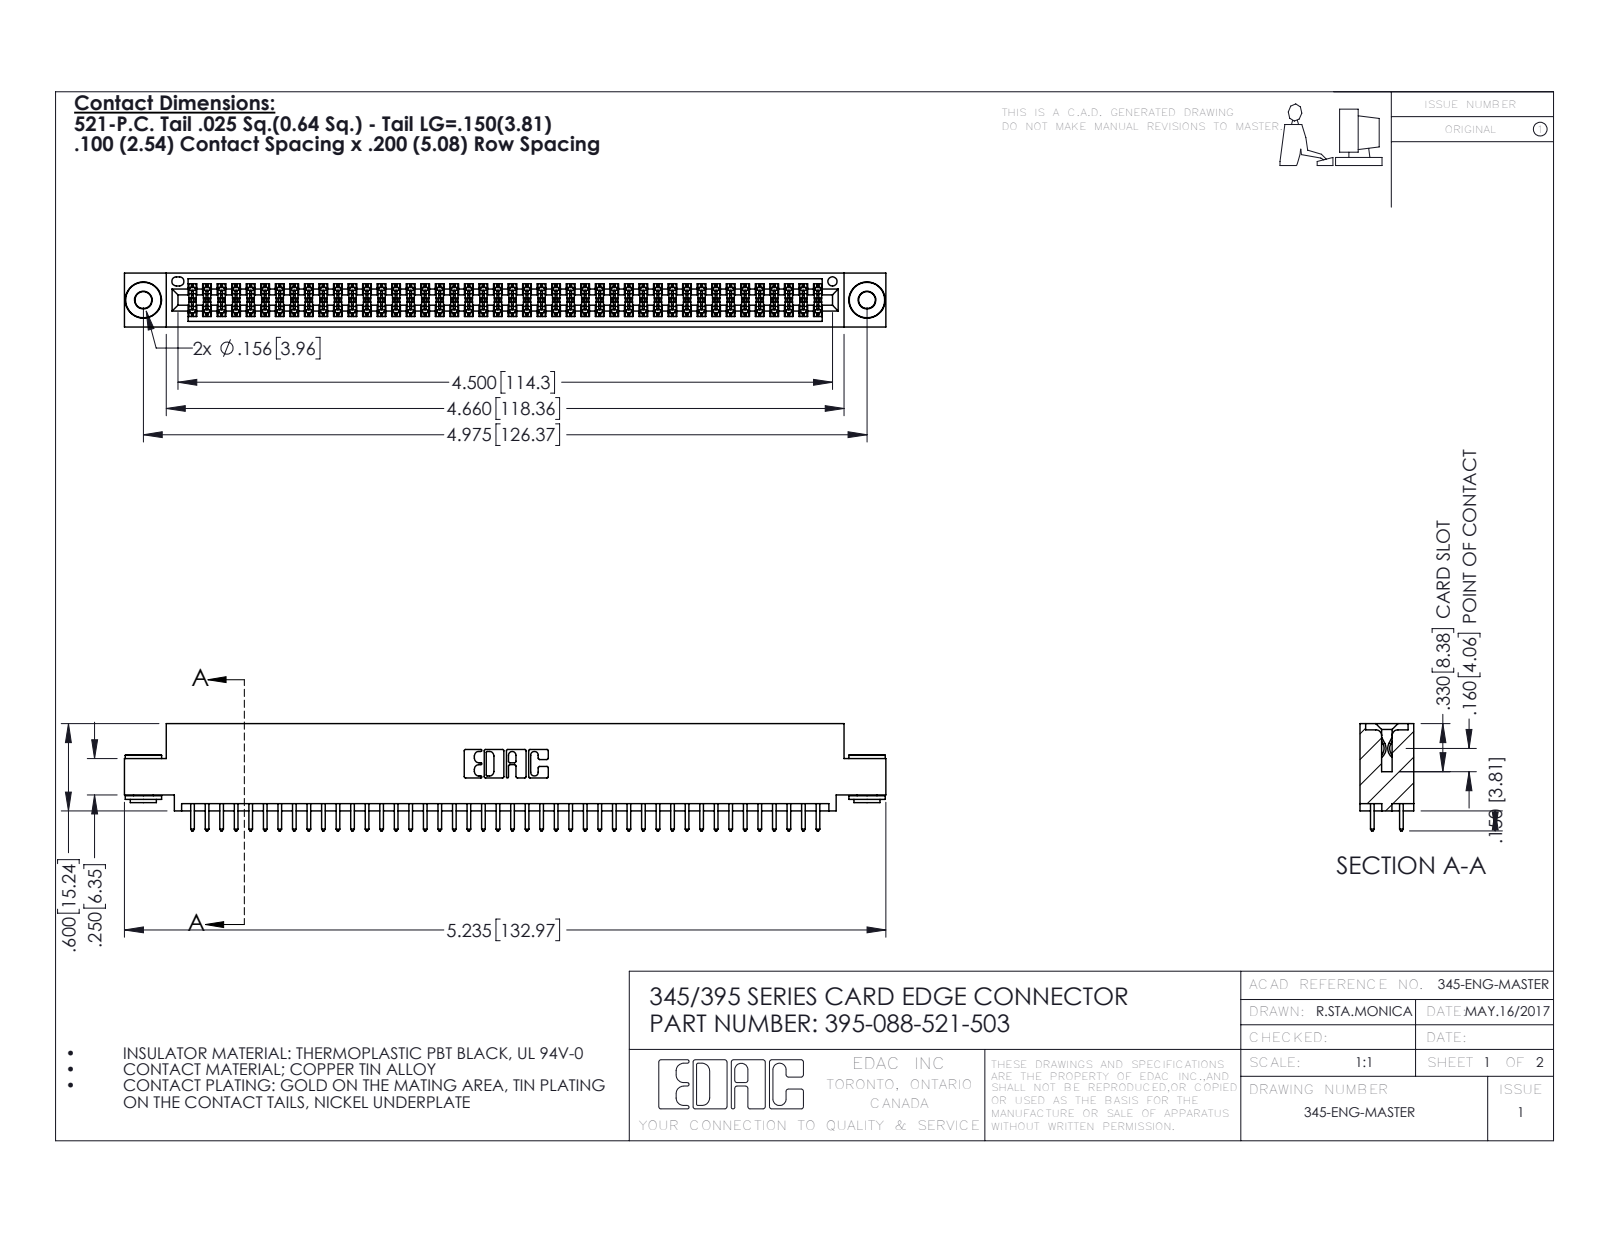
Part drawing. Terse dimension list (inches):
name: 395-088-521-503; 345-292-001_345-293-121; 345-250-002_345-250-002-102; 345 Part_0.110 Offset - 0.156 Dia-TH
written by: SolidWorks 2016 (CONFIG_CONTROL_DESIGN)
unit: in
bodies: 91 solids, 4568 faces (2998 planar, 1562 cylindrical, 8 other)
size: 5.235 × 0.737 × 0.37
volume: 0.784 in³; area: 29.59 in²
holes: 2× ⌀0.116, 2× ⌀0.156, 1× ⌀0.064
bosses: 2× ⌀0.25, 2× ⌀0.18, 2× ⌀0.136
rounds: 132× R0.006, 88× R0.01, 22× R0.01, 6× R0.007, 6× R0.031, 3× R0.026, 2× R0.014, 2× R0.019
face distances: 0.072, 0.298, 0.2, 0.025, 0.37, 0.098, 0.272, 0.225, 0.175, 0.149
hole spacings: 0.27, 4.739, 4.975
